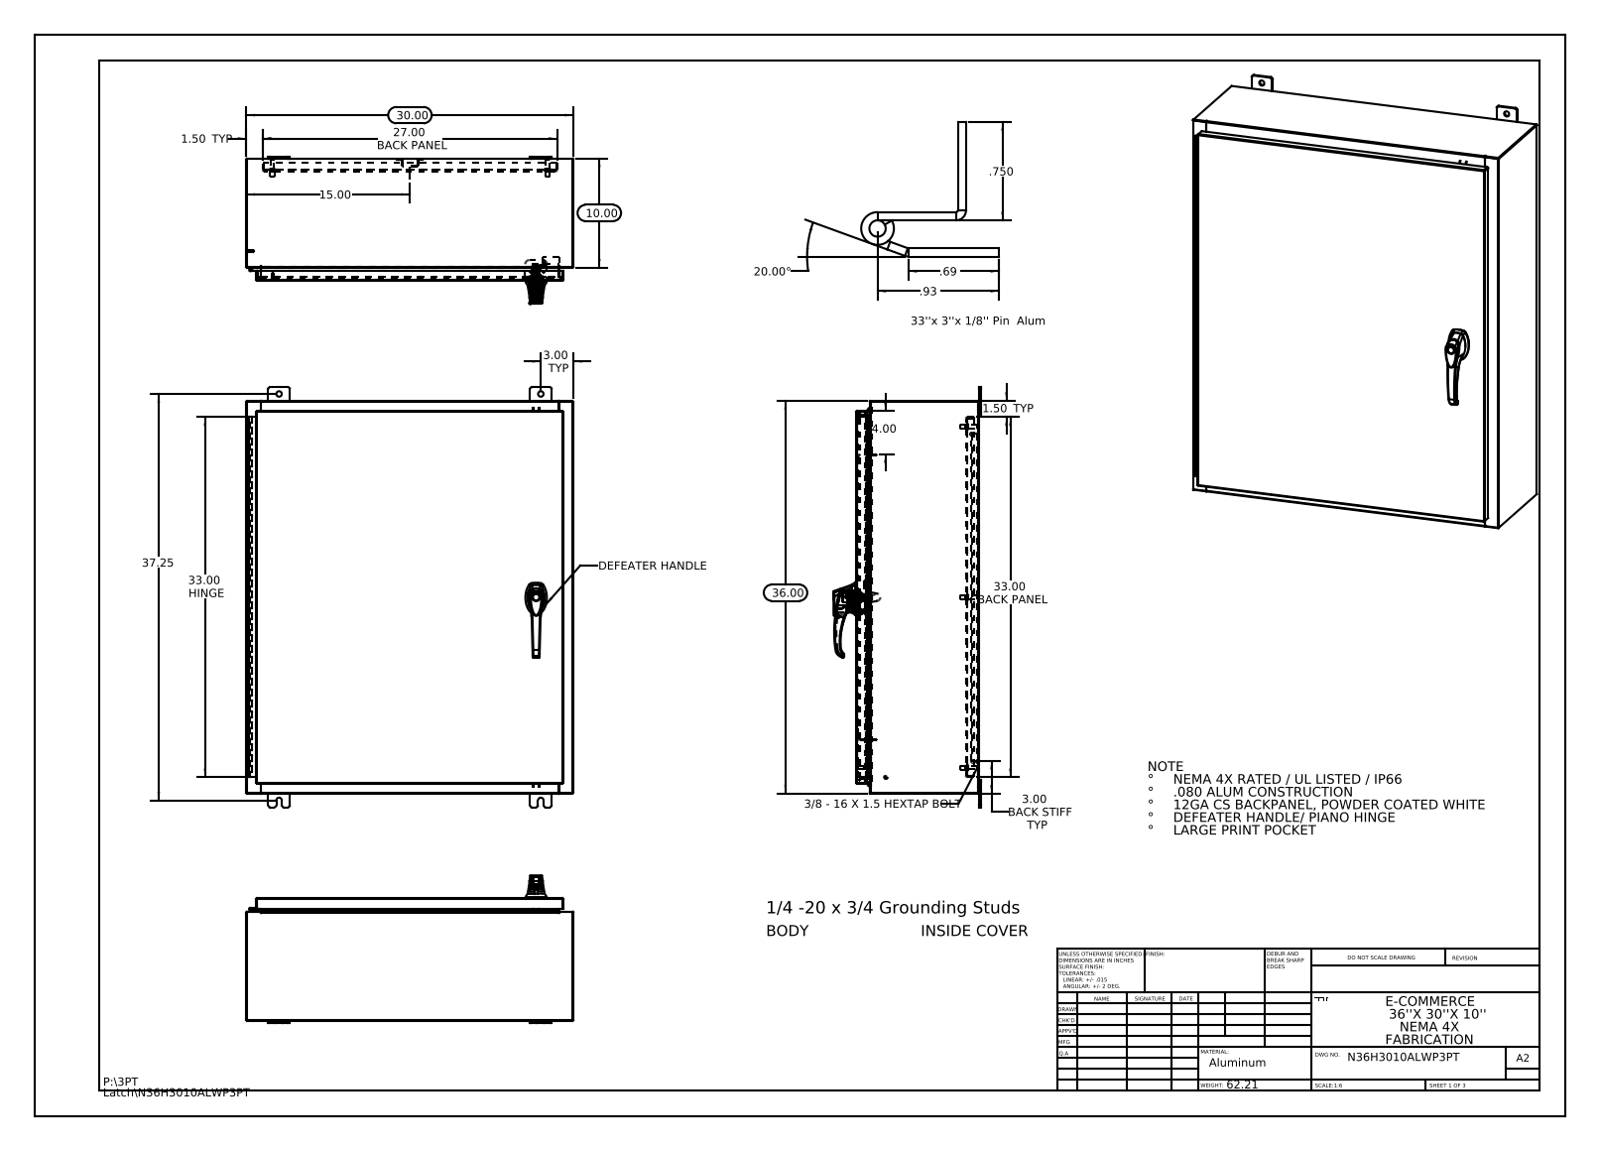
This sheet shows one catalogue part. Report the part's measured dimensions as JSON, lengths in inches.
{"part_name": "N36H3010ALWP3PT Hinge Cover Side; 022151; N36H3010ALWP3PT Defeater Handle Rod; N36H3010ALWP3PT Hinge Enclosure Side2 (+8 more)", "step_written_by": "SolidWorks 2013 (CONFIG_CONTROL_DESIGN)", "units": "inches", "bodies": {"solids": 40, "faces": 2894, "planar": 1083, "cylindrical": 1093, "other": 718}, "overall_size": [38.5, 30, 13.495], "volume_in3": 409, "surface_area_in2": 10131, "round_holes": [[0.5, 10], [0.25, 4], [0.138, 3], [0.161, 3], [0.079, 2], [0.203, 2], [0.313, 2], [0.437, 2], [0.125, 1], [0.125, 1], [0.197, 1], [0.276, 1]], "round_bosses_or_shafts": [[0.625, 6], [0.375, 6], [0.33, 6], [0.157, 4], [0.14, 4], [0.315, 3], [0.236, 3], [1.181, 1]], "partial_cylinders_radius": [[0.118, 37], [0.006, 33], [0.013, 28], [0.19, 24], [0.088, 22], [0.039, 15], [0.028, 12], [0.008, 6]], "face_to_face_distances": [0.075, 11.126, 11.051, 0.104, 11.201, 1, 10.126, 1.075, 10.051, 1.179], "hole_center_spacings": [11.363, 13.669, 15.625, 29.694, 25.25, 28.129, 0.295, 0.625]}
